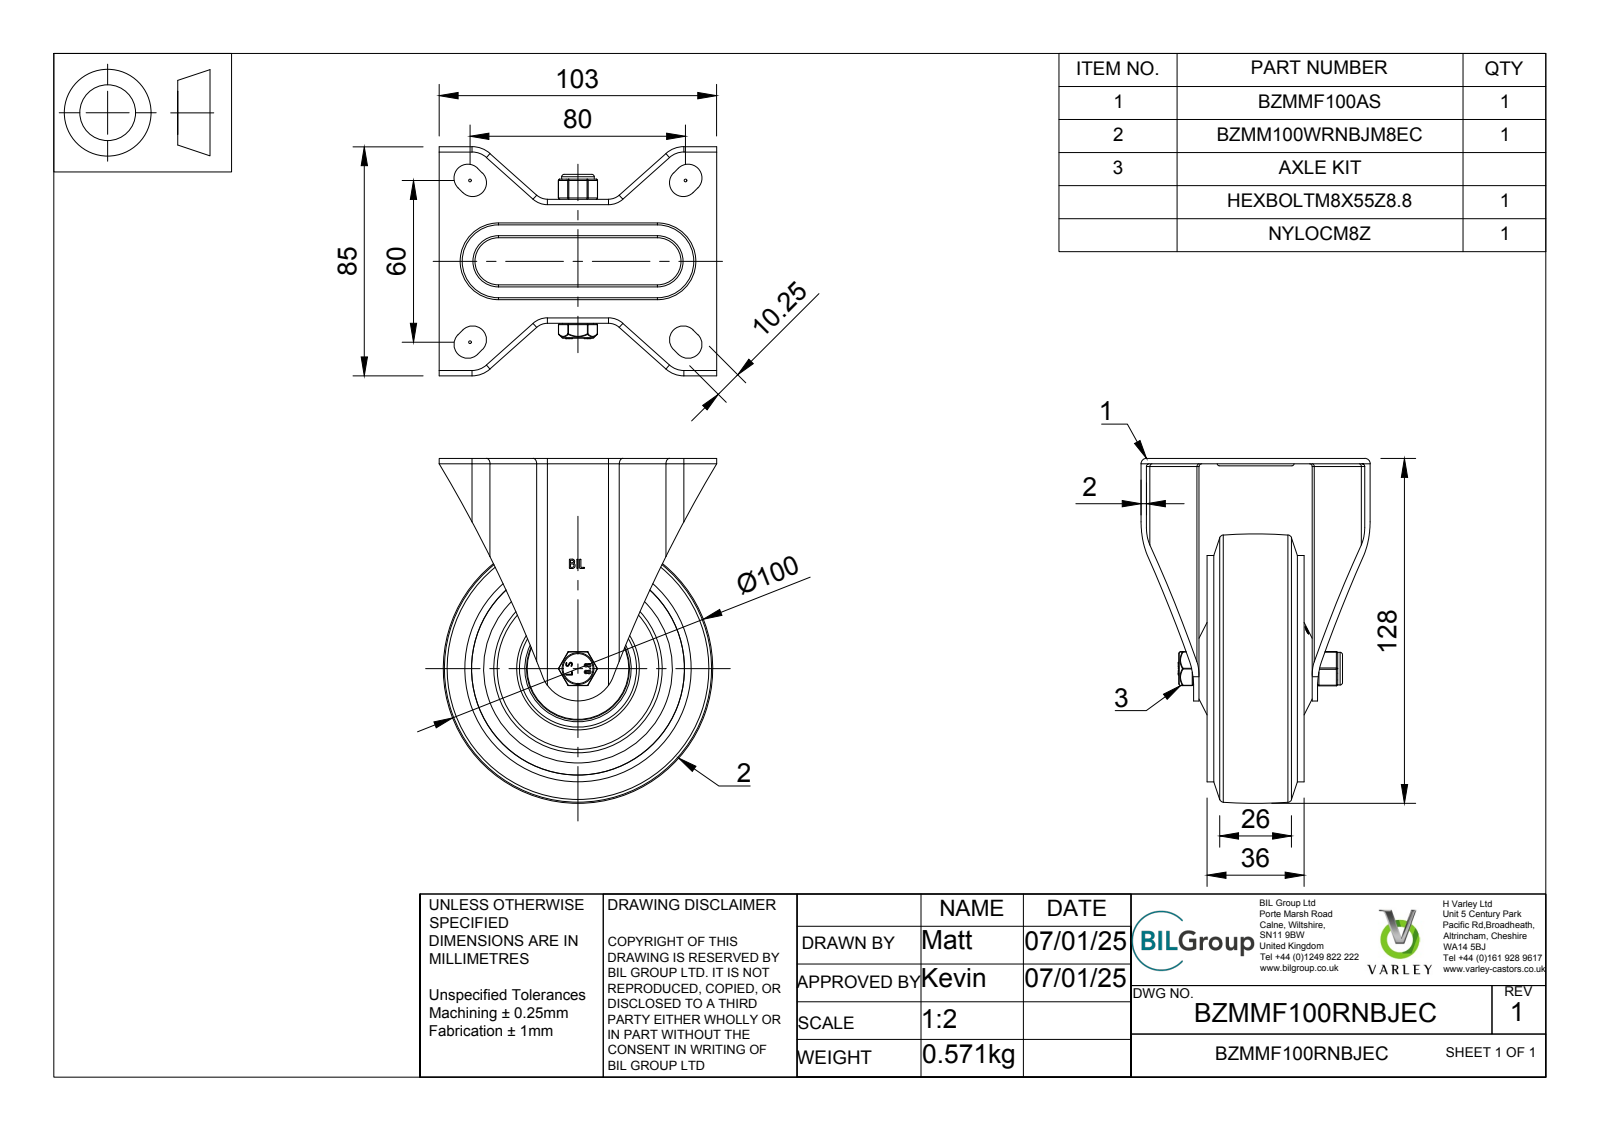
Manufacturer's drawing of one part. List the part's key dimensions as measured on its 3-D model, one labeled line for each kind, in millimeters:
Part name (STEP PRODUCT): BZMMF100RNBJEC v3; BZMMF100AS - 42 v1; ZINC PLATED, PRESSED STEEL BRACKET; BZMM100WRNBJM8EC v1 (+8 more)
STEP written by: Autodesk Translation Framework v13.20.0.188 (AP242_MANAGED_MODEL_BASED_3D_ENGINEERING_MIM_LF)
Units: millimetres
Bodies: 24 solids, 788 faces (281 planar, 228 cylindrical, 279 other)
Overall size (bounding box): 128 × 103 × 85
Volume: 225 744 mm³ · Surface area: 115 992 mm²
Round holes (diameter × count): ⌀0.66 ×2, ⌀3 ×2, ⌀4 ×1, ⌀8 ×1, ⌀8.2 ×1, ⌀8.25 ×1, ⌀8.6 ×1, ⌀15 ×1, ⌀20 ×1, ⌀22.5 ×1, ⌀26 ×1, ⌀30 ×1
Round bosses / shafts (diameter × count): ⌀84 ×1, ⌀43.5 ×1, ⌀38.25 ×1, ⌀34.5 ×1, ⌀30.5 ×1, ⌀28 ×1, ⌀23 ×1, ⌀19.5 ×1
Partial cylindrical surfaces — rounded edges, fillets, slot ends (radius × count): R0.5 ×18, R0.25 ×12, R0.75 ×8, R1 ×8, R2 ×8, R5.12 ×8, R0.33 ×4, R0.64 ×4
Main face-to-face distances: 2, 14.26, 5, 39, 44, 3, 41, 18.25, 25.75, 20.75
Hole centre spacings: 2.49, 3.21, 3.22
